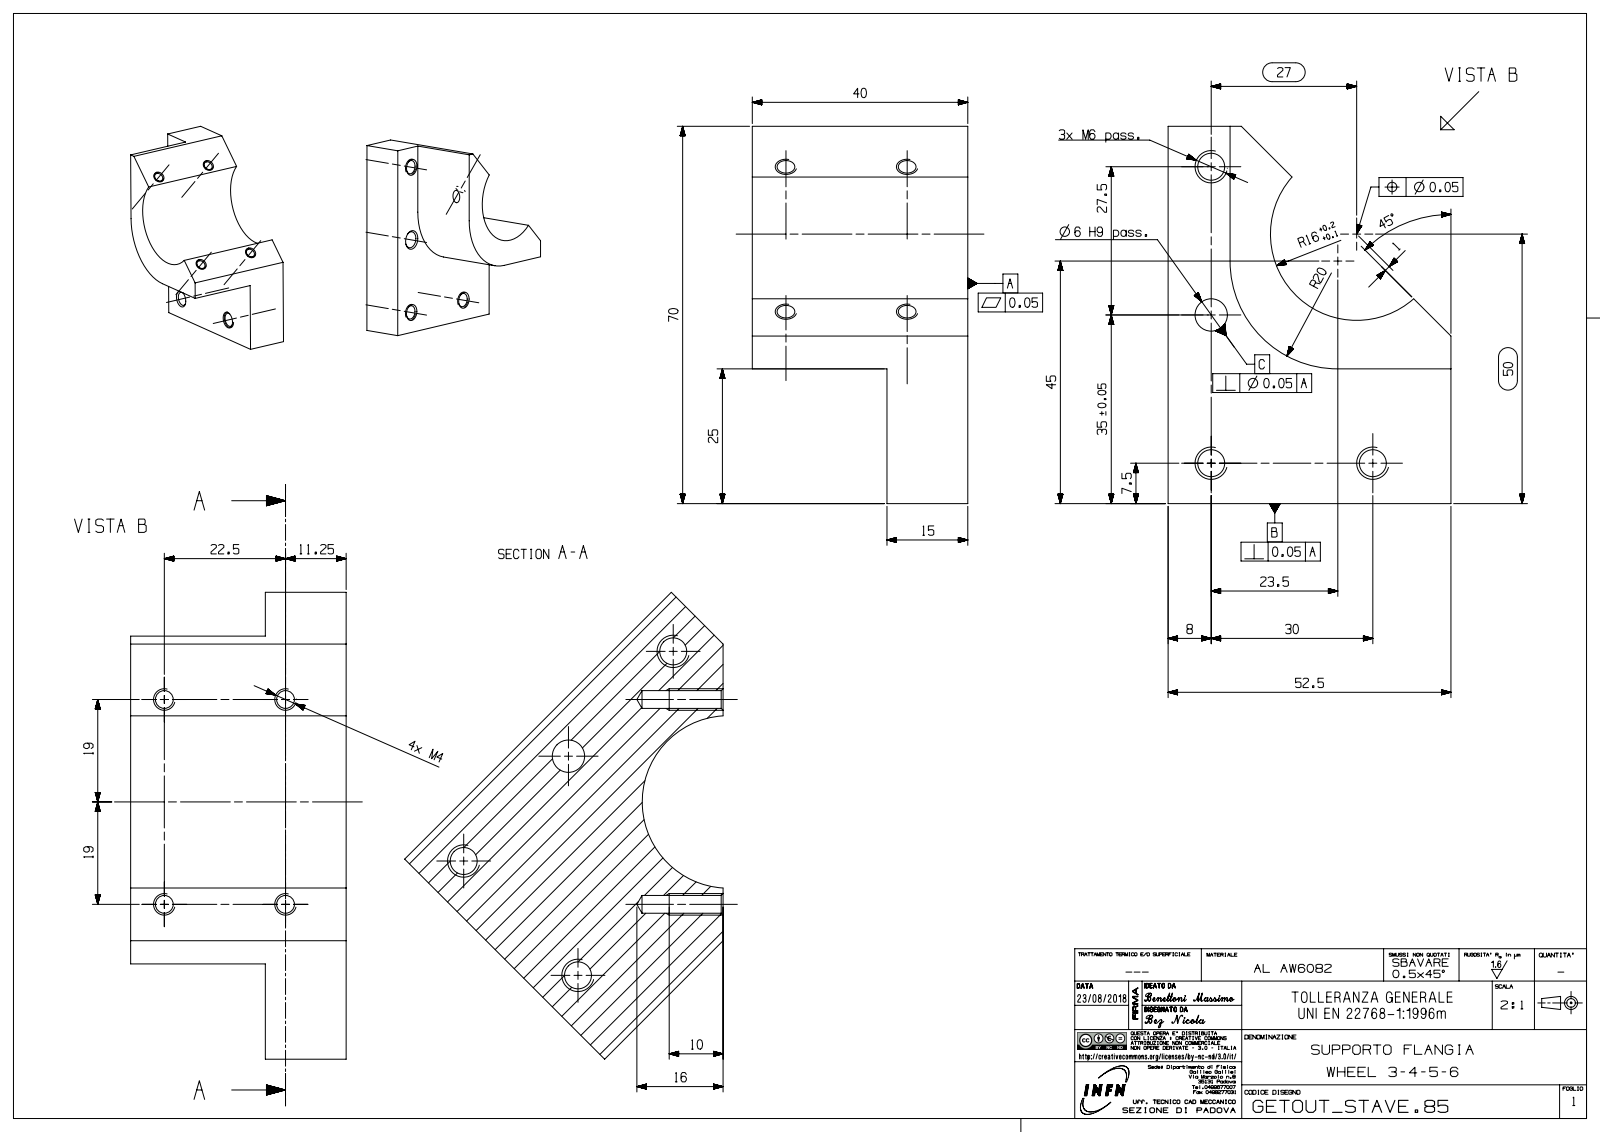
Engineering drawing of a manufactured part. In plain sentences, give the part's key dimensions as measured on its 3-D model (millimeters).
The part is named "bez8324385A6uwh". Its 3-D file was written by "SIEMENS PLM Software NX 12.0 (AUTOMOTIVE_DESIGN)". It is 1 solid with 35 faces: 11 planar, 10 cylindrical and 14 other. Overall it measures 70 by 52.5 by 40 millimeters. Its volume is 52 177 cubic millimeters and its surface area 13 938 square millimeters. Round holes: 4 of diameter 3.3, 3 of diameter 5, 1 of diameter 6. Partial cylindrical surfaces (rounded edges, fillets, slot ends): 1 of radius 16, 1 of radius 20. The main face-to-face distances are 15, 25, 40, 52.5, 41, 11.5, 70, 45. The hole center spacings are 22.5, 27.5, 38, 44.16, 30, 40.7, 55, 62.65.
